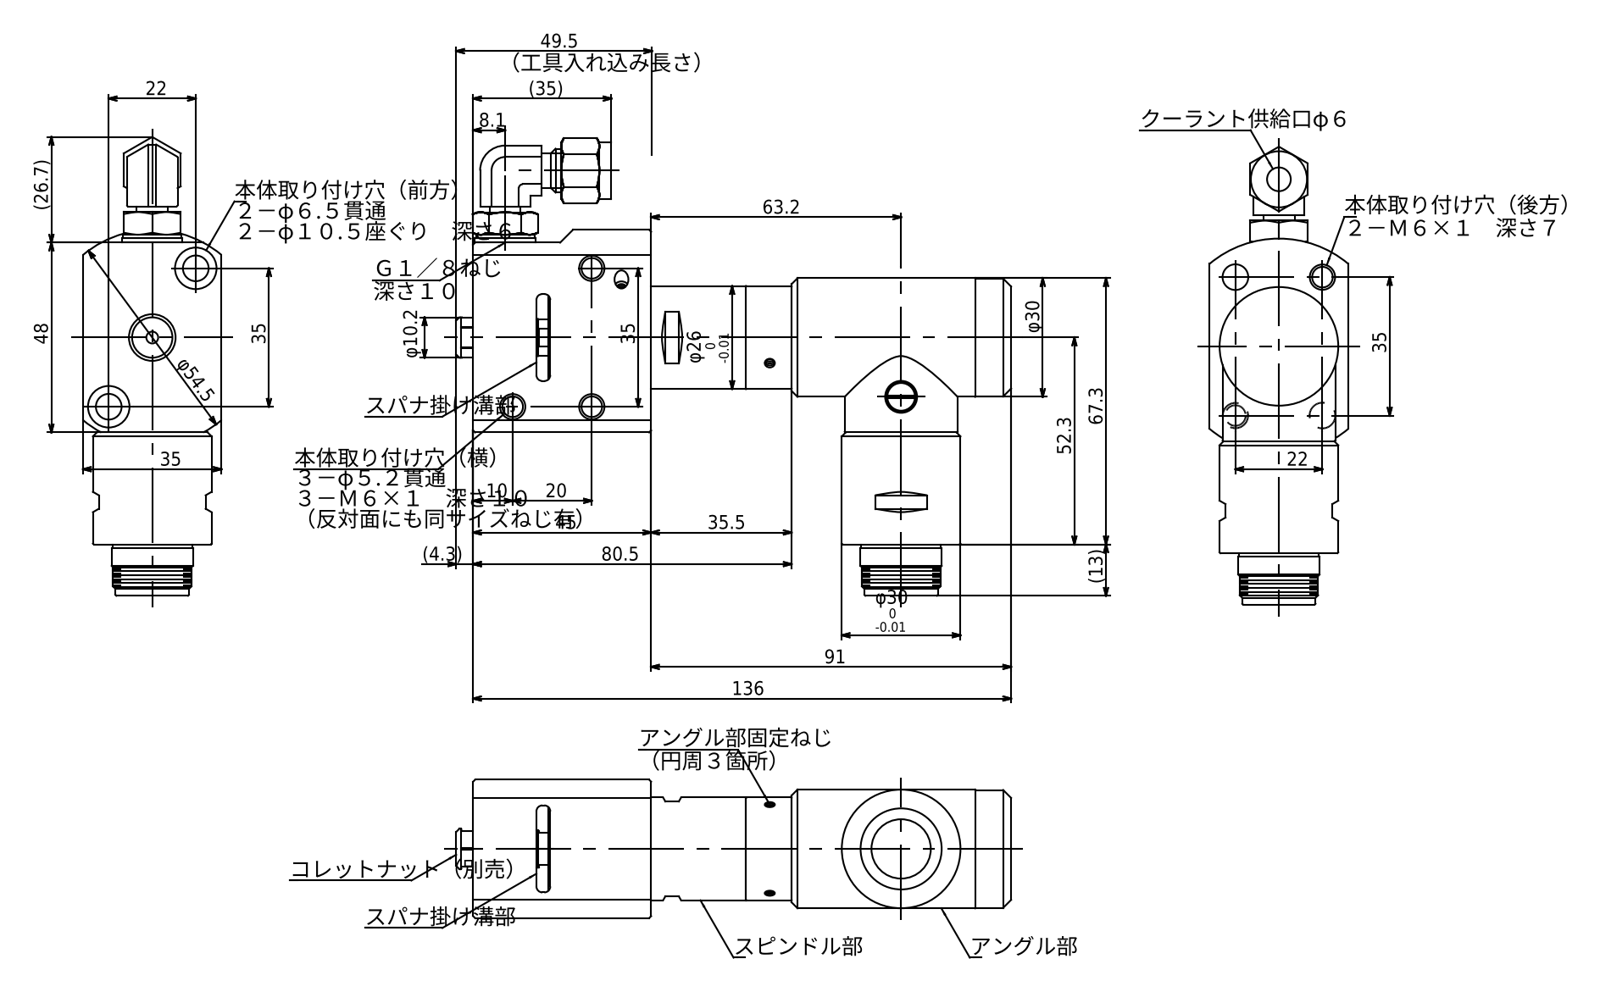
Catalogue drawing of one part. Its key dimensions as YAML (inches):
part_name: "CTS-2620A"
step_written_by: "SolidWorks 2021 (CONFIG_CONTROL_DESIGN)"
units: inches
bodies: {solids: 0, faces: 554, planar: 260, cylindrical: 143, other: 151}
overall_size: [5.522, 4.553, 1.378]
round_holes:
  - {diameter: 0.063, count: 6}
  - {diameter: 0.098, count: 3}
  - {diameter: 0.1, count: 3}
  - {diameter: 0.138, count: 3}
  - {diameter: 0.205, count: 3}
  - {diameter: 0.079, count: 2}
  - {diameter: 0.157, count: 2}
  - {diameter: 0.201, count: 2}
  - {diameter: 0.236, count: 2}
  - {diameter: 0.256, count: 2}
  - {diameter: 0.413, count: 2}
  - {diameter: 1.142, count: 2}
round_bosses_or_shafts:
  - {diameter: 0.118, count: 3}
  - {diameter: 1.217, count: 1}
  - {diameter: 1.181, count: 1}
  - {diameter: 1.173, count: 1}
  - {diameter: 1.024, count: 1}
  - {diameter: 1.022, count: 1}
  - {diameter: 0.976, count: 1}
  - {diameter: 0.807, count: 1}
partial_cylinders:
  - {radius: 0.059, count: 10}
  - {radius: 0.043, count: 4}
  - {radius: 0.069, count: 2}
  - {radius: 0.25, count: 1}
  - {radius: 1.073, count: 1}
face_to_face_distances: [1.378, 1.772, 0.118, 1.654, 1.89, 5.354, 5.236, 3.583, 0.138, 0.02]
hole_center_spacings: [0.453, 0.503, 0.547, 0.555, 0.659, 0.7, 0.704, 0.785]
